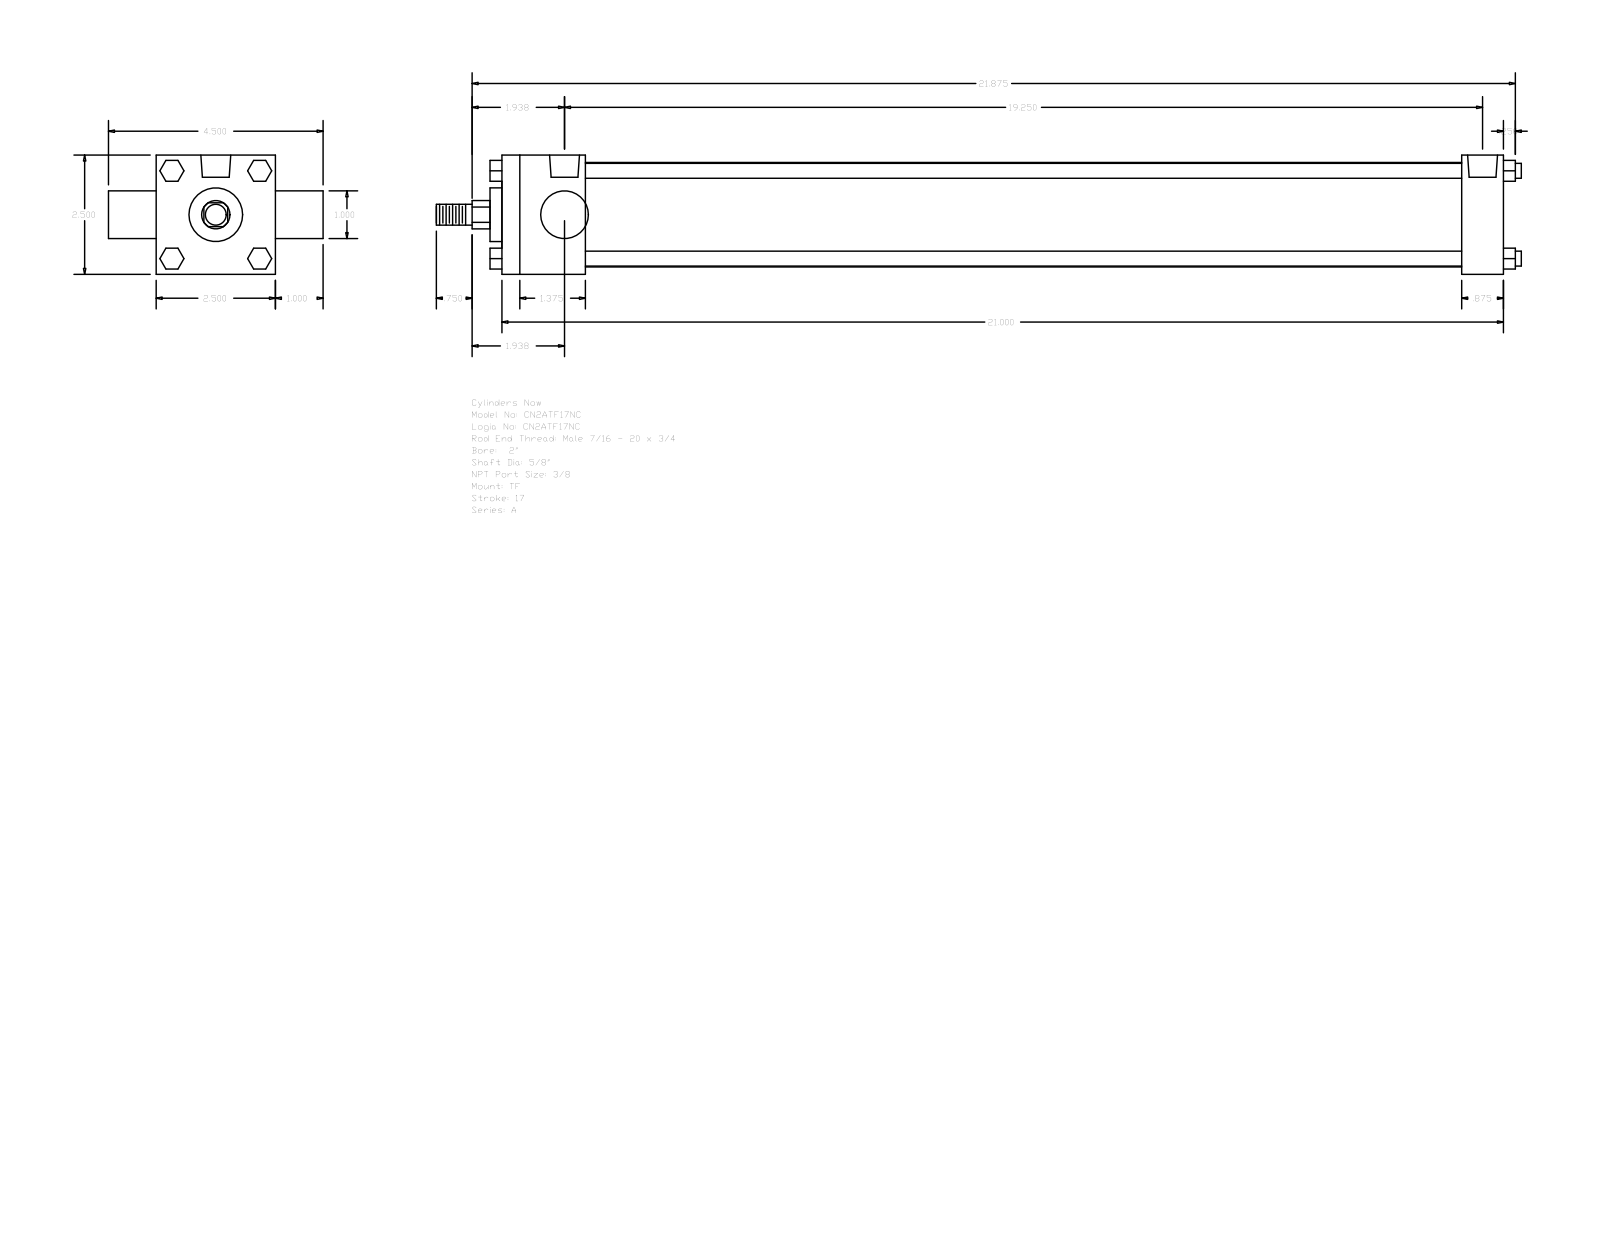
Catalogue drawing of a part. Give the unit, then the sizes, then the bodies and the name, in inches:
Units: inches
Overall size (bounding box): 22.75 × 4.5 × 2.5
Round holes (diameter × count): ⌀0.219 ×3, ⌀0.627 ×2
Round bosses / shafts (diameter × count): ⌀0.313 ×4, ⌀2.19 ×1, ⌀1.125 ×1, ⌀1 ×1, ⌀0.625 ×1, ⌀0.437 ×1
Partial cylindrical surfaces — rounded edges, fillets, slot ends (radius × count): R0.297 ×1
Main face-to-face distances: 2.5, 21, 1.75, 20.125, 18.375, 19.25, 0.875, 1, 3.5, 0.25
Hole centre spacings: 0.156, 0.157, 18.937, 19.093, 19.094, 19.25
Bodies: 0 solids, 120 faces (92 planar, 28 cylindrical, 0 other)
Part name (STEP PRODUCT): A_TF__0200_0.625
STEP written by: GSSL Pune (CONFIG_CONTROL_DESIGN)
